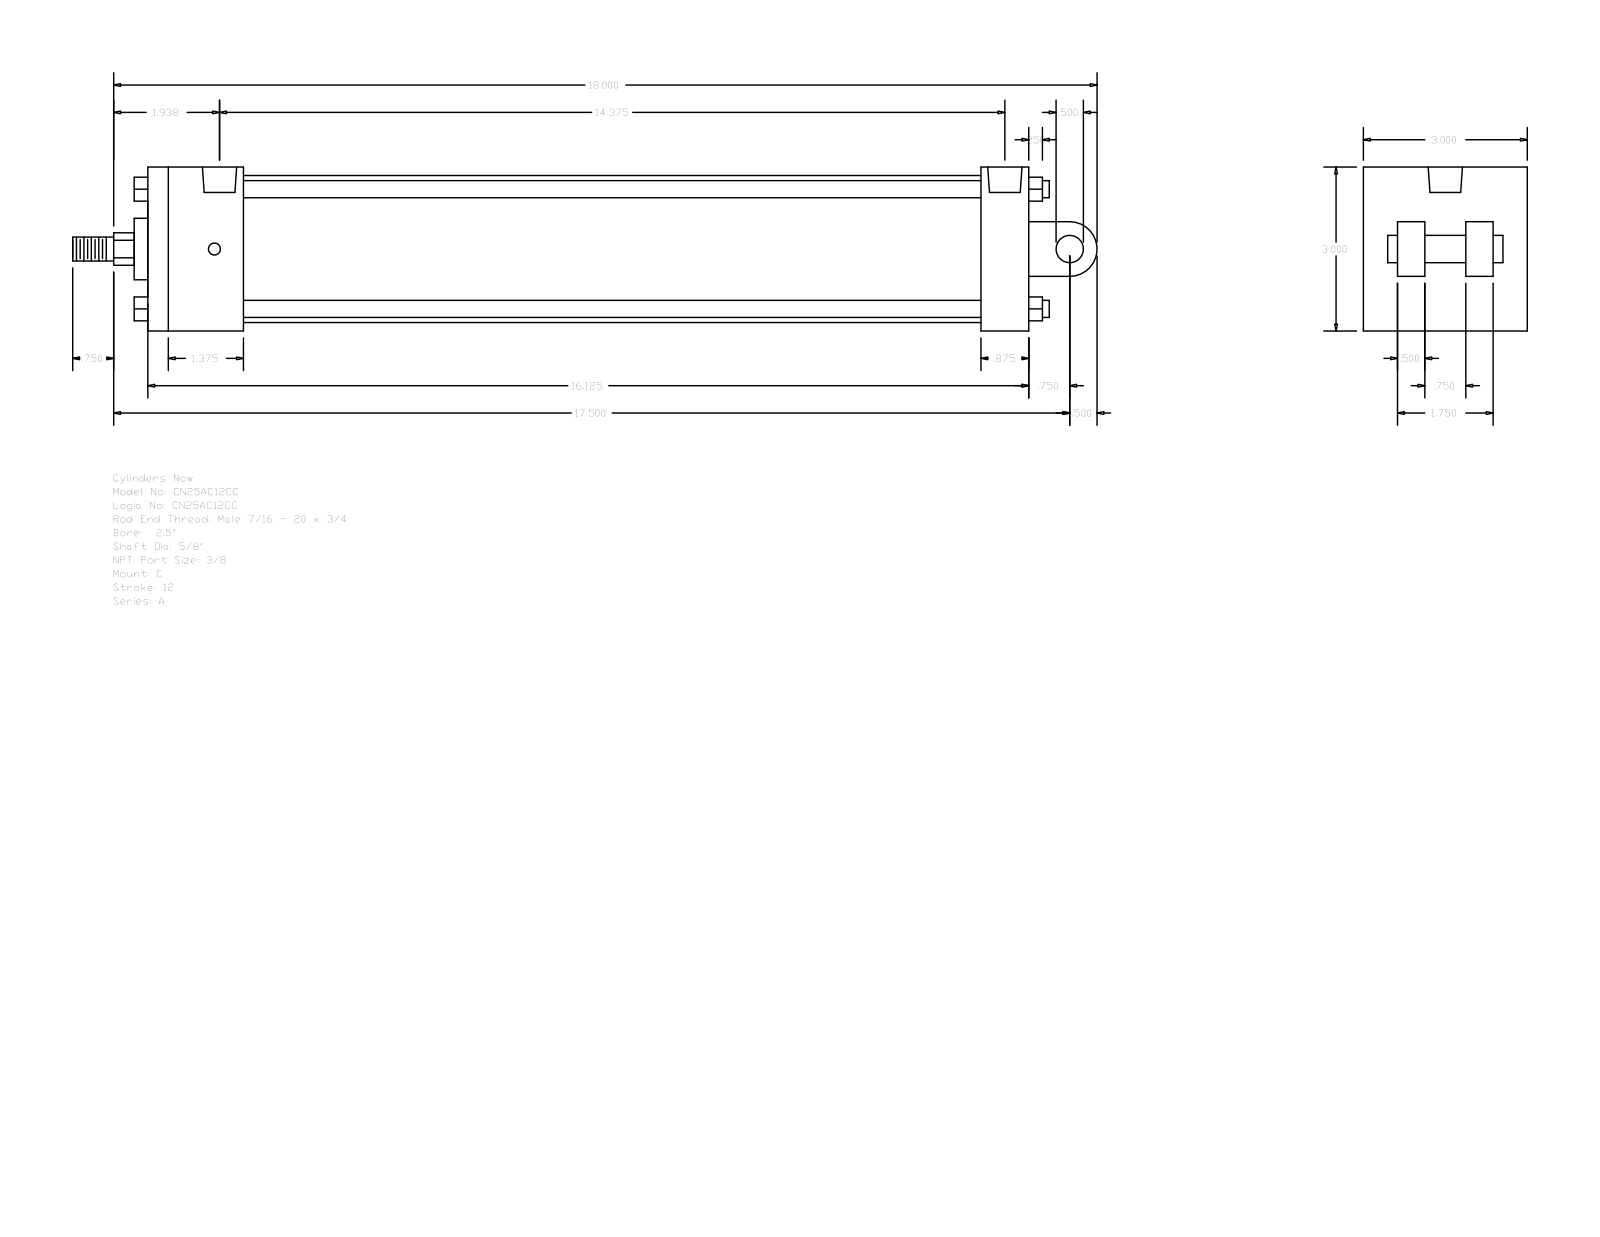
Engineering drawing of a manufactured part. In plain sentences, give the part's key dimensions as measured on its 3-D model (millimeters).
The part is named "A_C__0250_0.625". Its 3-D file was written by "GSSL Pune (CONFIG_CONTROL_DESIGN)". It is 0 solids with 135 faces: 102 planar, 33 cylindrical and 0 other. Overall it measures 476.25 by 76.2 by 76.2 millimeters. Round holes: 4 of diameter 5.56, 2 of diameter 15.93. Round bosses or shafts: 4 of diameter 7.94, 1 of diameter 68.33, 1 of diameter 28.57, 1 of diameter 15.88, 1 of diameter 12.7, 1 of diameter 11.11. Partial cylindrical surfaces (rounded edges, fillets, slot ends): 1 of radius 7.54, 1 of radius 12.7. The main face-to-face distances are 76.2, 409.57, 44.45, 387.35, 342.9, 365.12, 22.22, 50.8, 12.7, 25.4. The hole center spacings are 2.38, 367.51, 369.89, 365.13.
